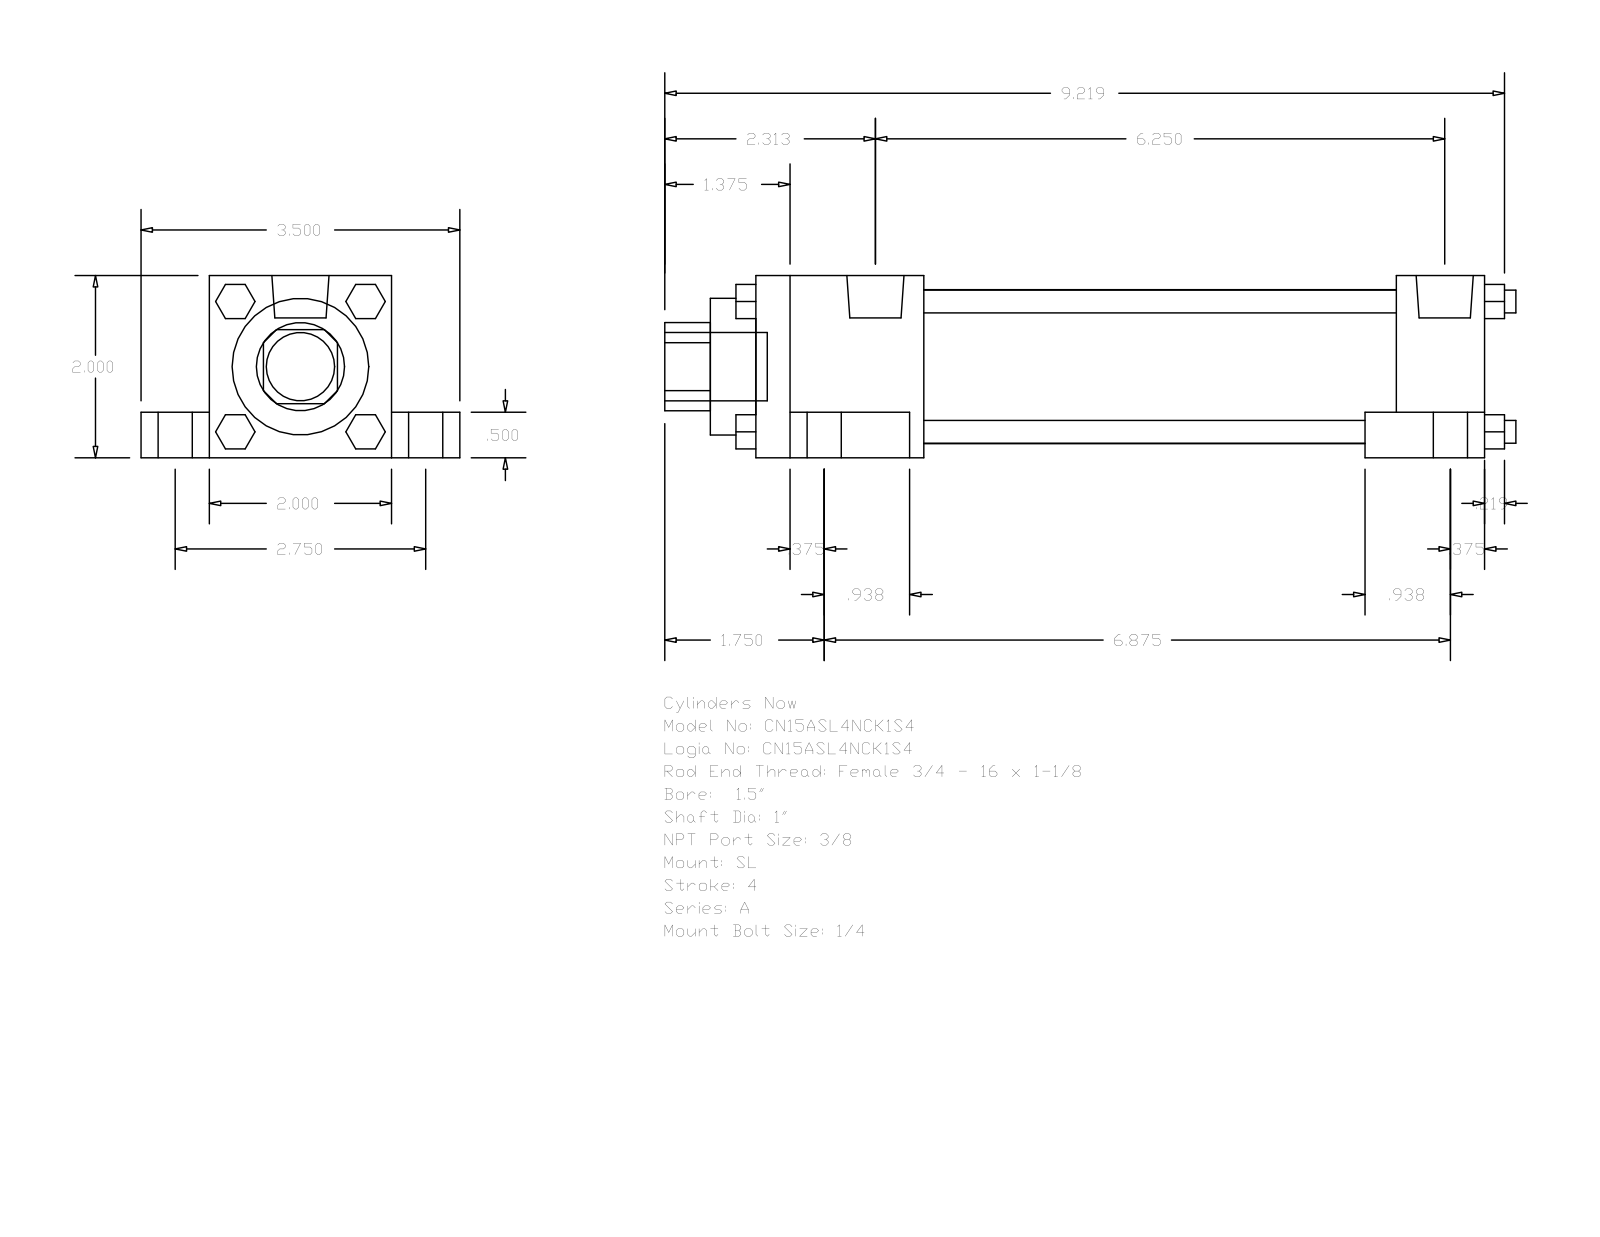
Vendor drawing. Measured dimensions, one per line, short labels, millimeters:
name: A_SL__0150_1
written by: GSSL Pune (CONFIG_CONTROL_DESIGN)
unit: mm
bodies: 0 solids, 148 faces (112 planar, 36 cylindrical, 0 other)
size: 237.33 × 88.9 × 50.8
holes: 1× ⌀25.4, 1× ⌀38.1, 1× ⌀42.93
bosses: 4× ⌀15.88, 4× ⌀9.53, 4× ⌀6.35, 4× ⌀5.56, 2× ⌀15.93, 1× ⌀19.05
rounds: 1× R12.29
face distances: 50.8, 12.7, 38.1, 19.05, 69.85, 9.52, 203.2, 33.34, 178.59, 24.61
